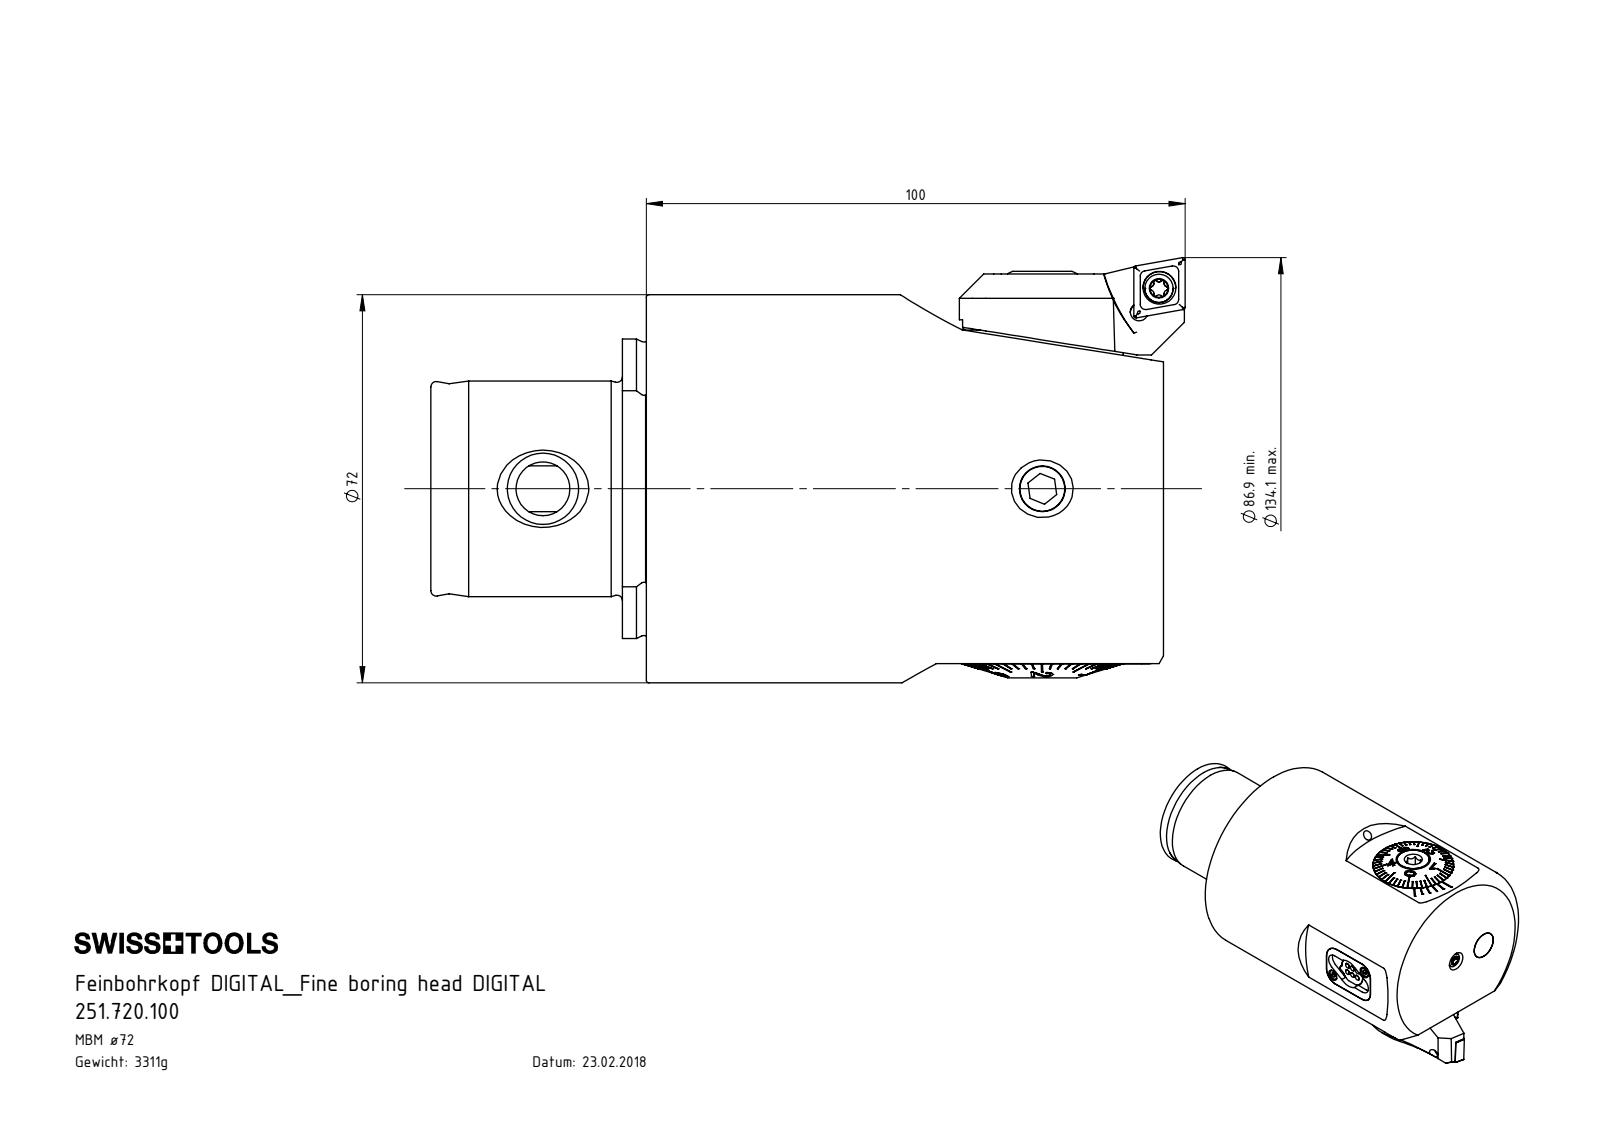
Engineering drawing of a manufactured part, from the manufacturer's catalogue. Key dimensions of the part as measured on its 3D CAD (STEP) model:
Part name (STEP PRODUCT): ISO 4026 - M10 x 16; F55-ER1.101.016_A; A55-BG3.011.033_A_gekrzt; A55-BG2.012.006_B (+8 more)
STEP written by: SolidWorks 2017 (AUTOMOTIVE_DESIGN)
Units: millimetres
Bodies: 25 solids, 864 faces (453 planar, 164 cylindrical, 247 other)
Overall size (bounding box): 140 × 78.89 × 72
Volume: 422 571 mm³ · Surface area: 71 645 mm²
Round holes (diameter × count): ⌀3.3 ×9, ⌀4.2 ×3, ⌀8.5 ×3, ⌀1.6 ×2, ⌀2.2 ×2, ⌀10 ×2, ⌀13 ×2, ⌀4.4 ×1, ⌀5 ×1, ⌀6.1 ×1, ⌀8 ×1, ⌀9.5 ×1
Round bosses / shafts (diameter × count): ⌀1.9 ×6, ⌀10 ×2, ⌀5.25 ×2, ⌀4 ×2, ⌀3.8 ×2, ⌀2 ×2, ⌀72 ×1, ⌀40 ×1
Partial cylindrical surfaces — rounded edges, fillets, slot ends (radius × count): R0.34 ×12, R0.59 ×12, R1.1 ×6, R1.2 ×6, R0.5 ×4, R4.5 ×4, R3.2 ×3, R4.4 ×3
Main face-to-face distances: 96, 40, 136, 55.8, 35.55, 4.45, 100.45, 2.5, 9, 62.28
Hole centre spacings: 9.52, 5.73, 5.86, 14.05, 14.5, 19.04, 26, 32.5
